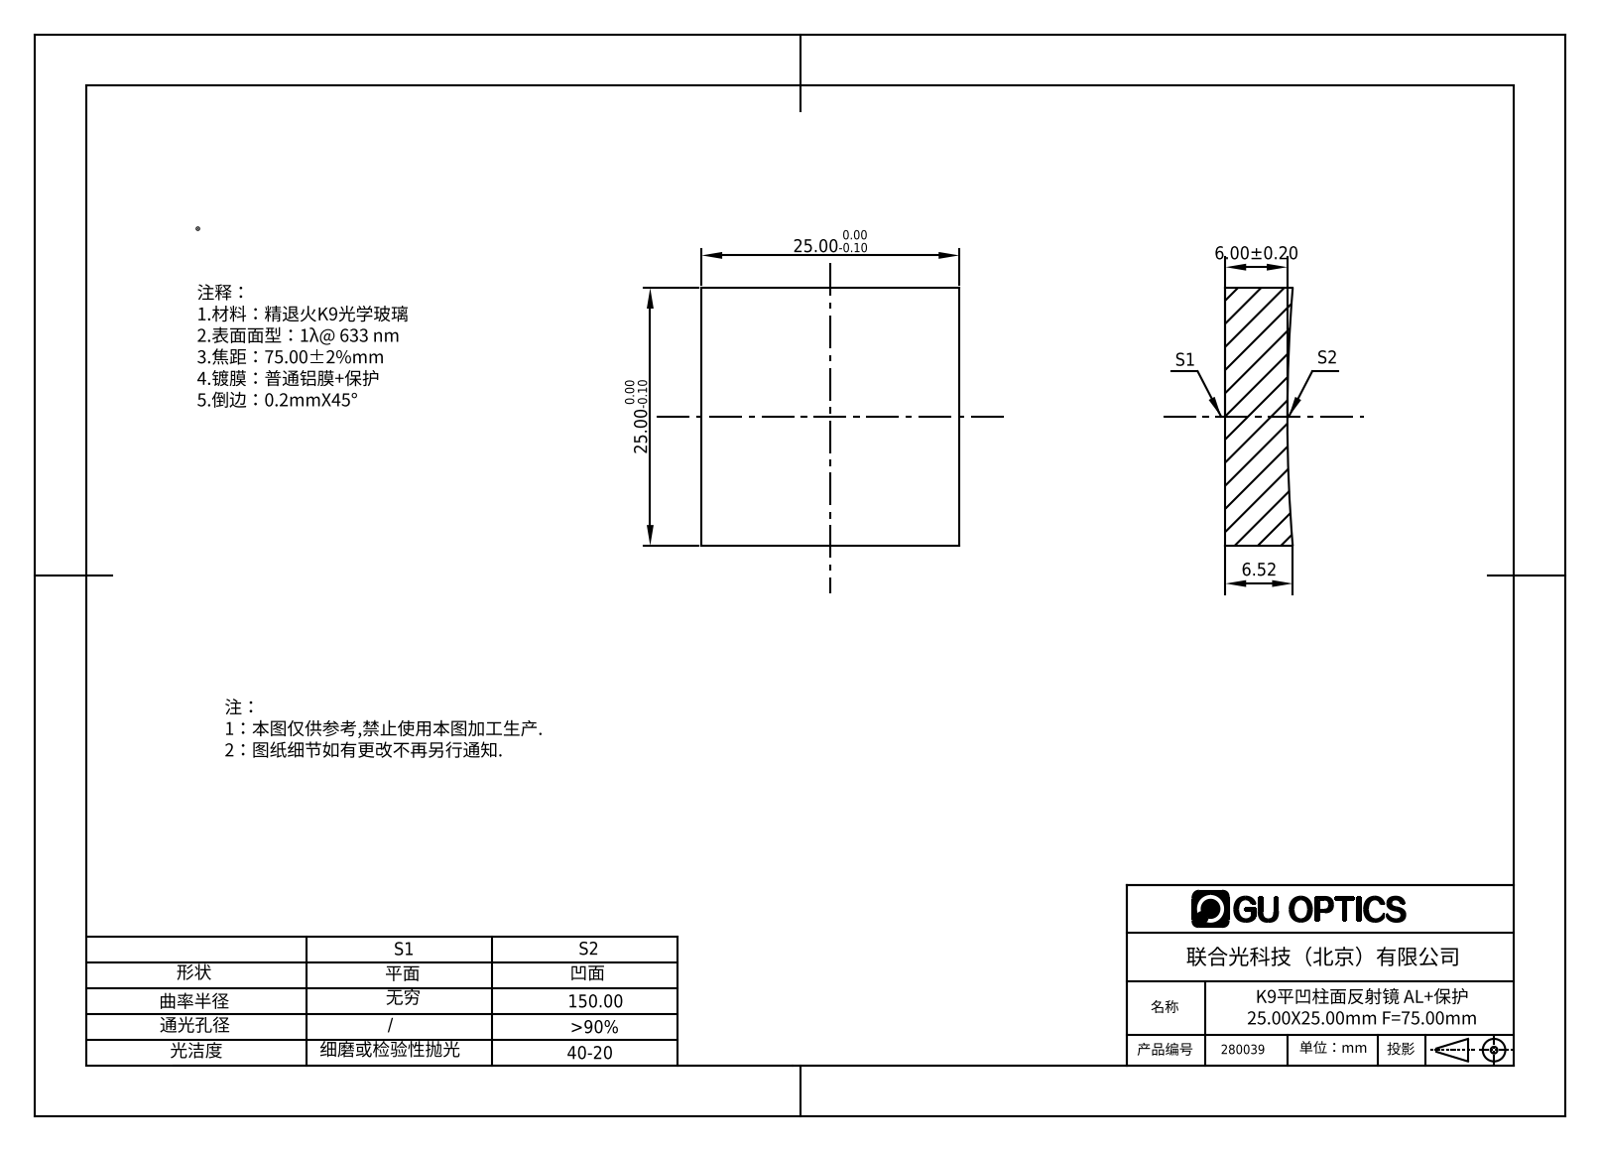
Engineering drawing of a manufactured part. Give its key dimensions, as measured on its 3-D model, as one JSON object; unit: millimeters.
{"part_name": "280017", "step_written_by": "SolidWorks 2016 (AUTOMOTIVE_DESIGN)", "units": "millimeters", "bodies": {"solids": 1, "faces": 7, "planar": 5, "cylindrical": 2, "other": 0}, "overall_size": [25, 25, 6.52], "volume_mm3": 3859, "surface_area_mm2": 1886, "partial_cylinders_radius": [[150, 1]], "face_to_face_distances": [25]}
